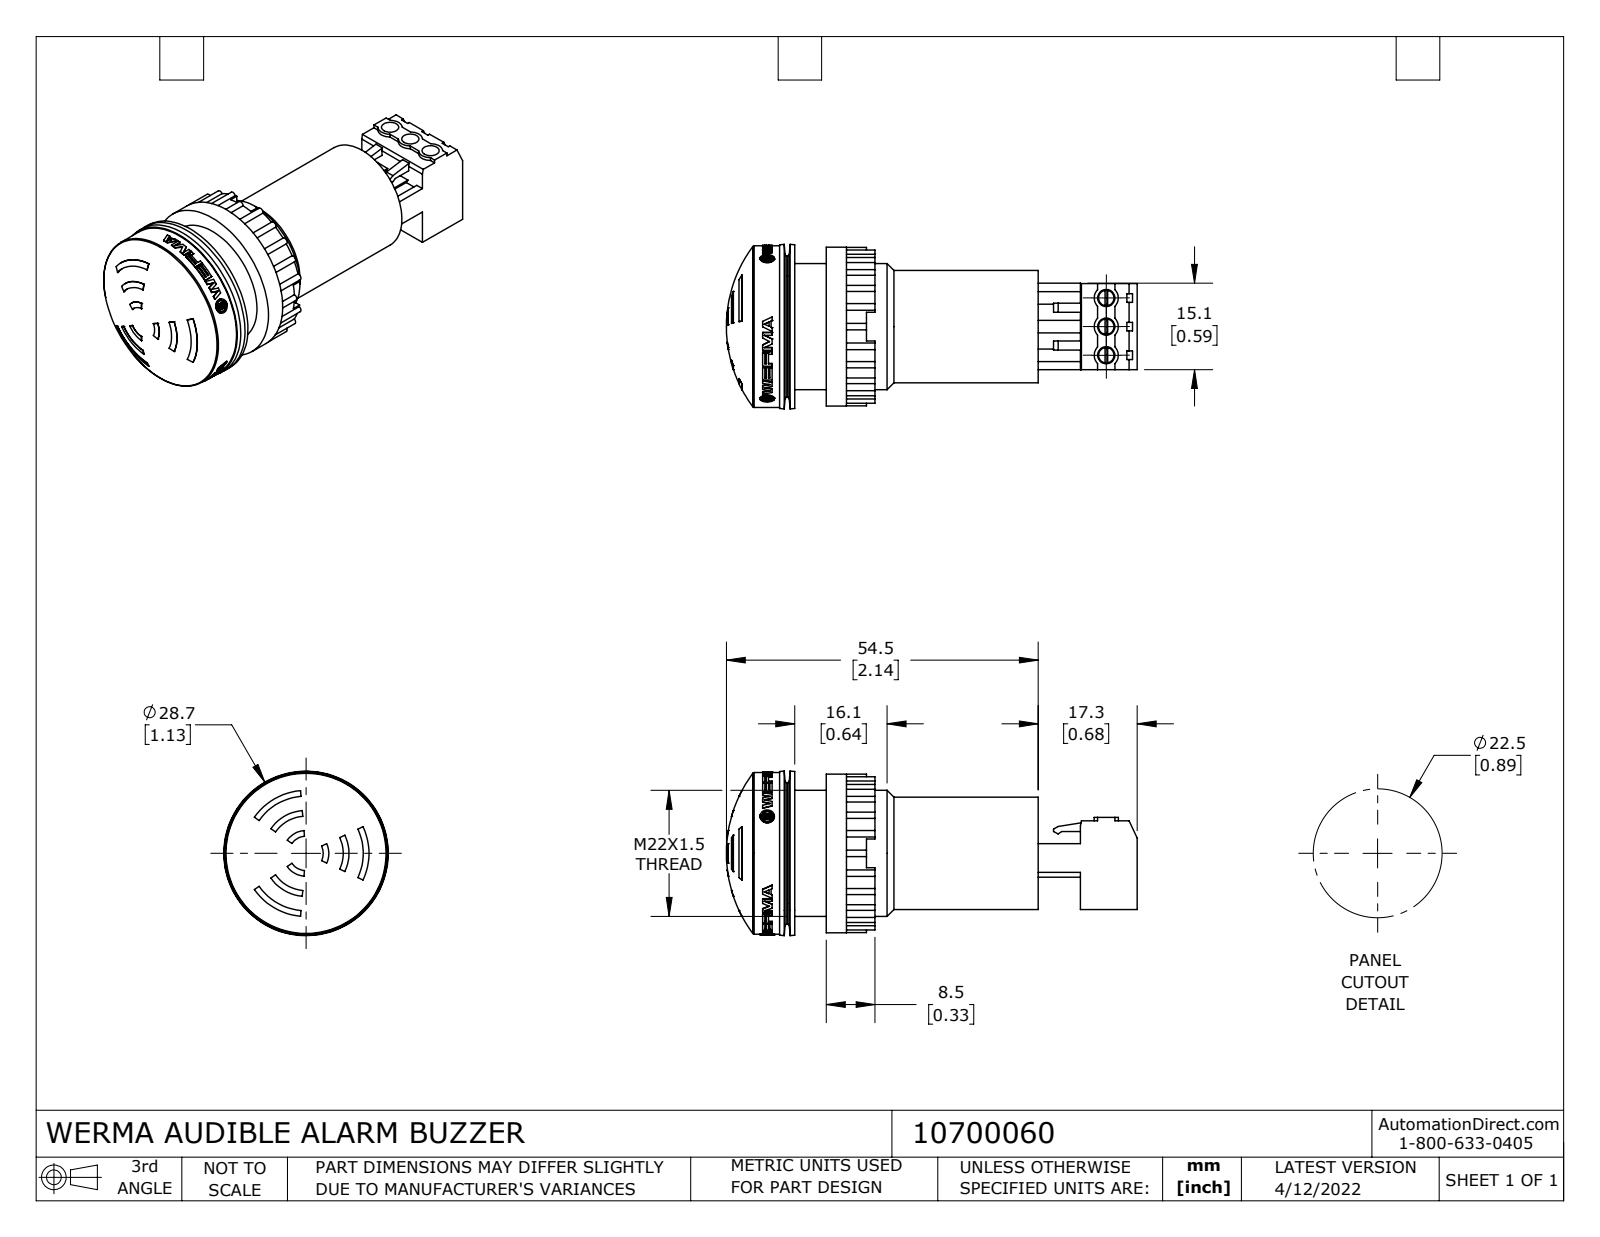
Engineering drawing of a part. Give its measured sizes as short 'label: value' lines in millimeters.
name: 10700060
written by: SolidWorks 2021 (CONFIG_CONTROL_DESIGN)
unit: mm
bodies: 1 solid, 617 faces (321 planar, 148 cylindrical, 148 other)
size: 71.6 × 28.7 × 28.7
volume: 24 330 mm³; area: 7 413 mm²
holes: 3× ⌀3
bosses: 3× ⌀2.7, 1× ⌀28.2, 1× ⌀27.7, 1× ⌀24.7, 1× ⌀22, 1× ⌀19.6
rounds: 24× R0.6, 3× R2.1, 3× R2.8, 1× R3, 1× R4, 1× R6.5, 1× R7.5, 1× R10
face distances: 37, 5, 15, 8.5, 7.4, 44.4, 35.9, 28.5, 9.9, 17.3
hole spacings: 5, 10
